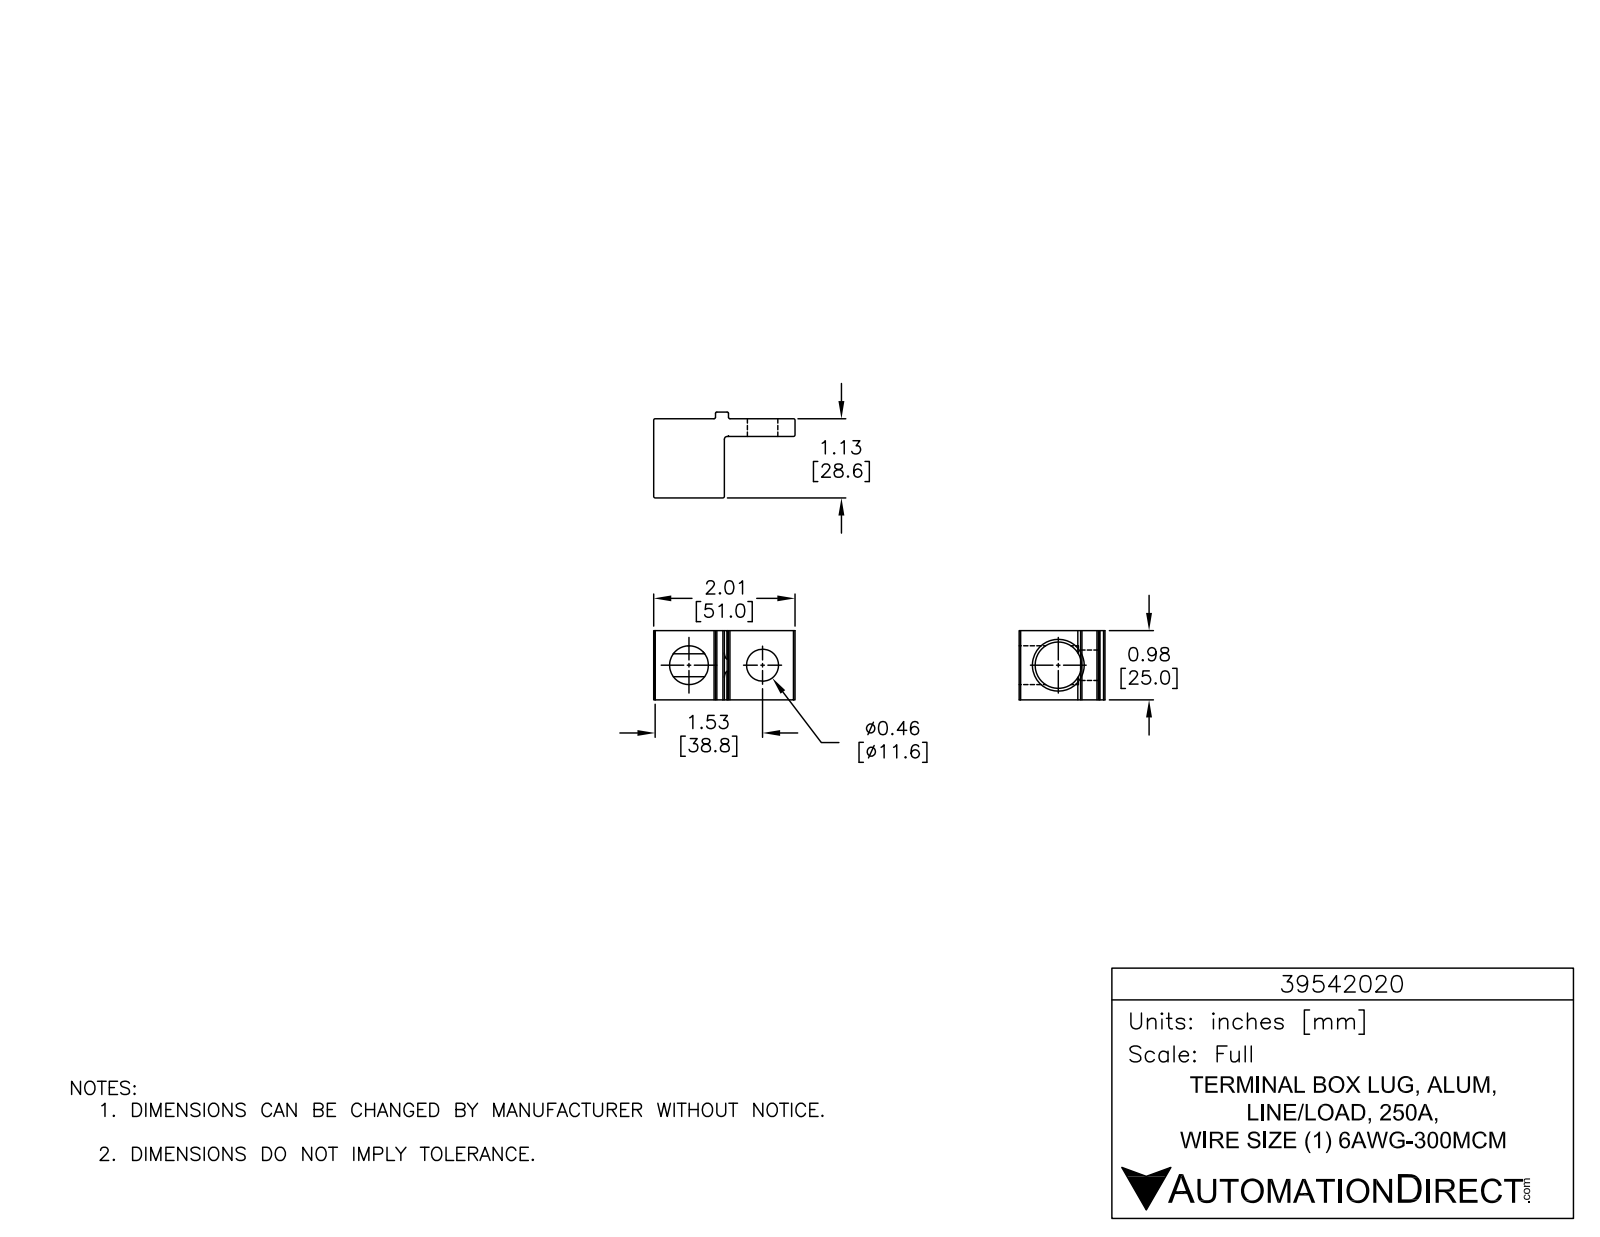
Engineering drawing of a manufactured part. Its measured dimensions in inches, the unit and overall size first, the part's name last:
Units: inches
Overall size (bounding box): 2.008 × 1.22 × 0.984
Round holes (diameter × count): ⌀0.433 ×1, ⌀0.551 ×1, ⌀0.657 ×1
Partial cylindrical surfaces — rounded edges, fillets, slot ends (radius × count): R0.02 ×9, R0.039 ×1
Main face-to-face distances: 0.984, 0.252, 1.126, 0.874, 1.004, 2.008, 0.094, 0.346, 1.22, 0.378
Hole centre spacings: 1.045
Volume: 0.934 in³ · Surface area: 10.52 in²
Bodies: 1 solid, 37 faces (15 planar, 20 cylindrical, 2 other)
Part name (STEP PRODUCT): 39542020
STEP written by: SolidWorks 2015 (AUTOMOTIVE_DESIGN)
